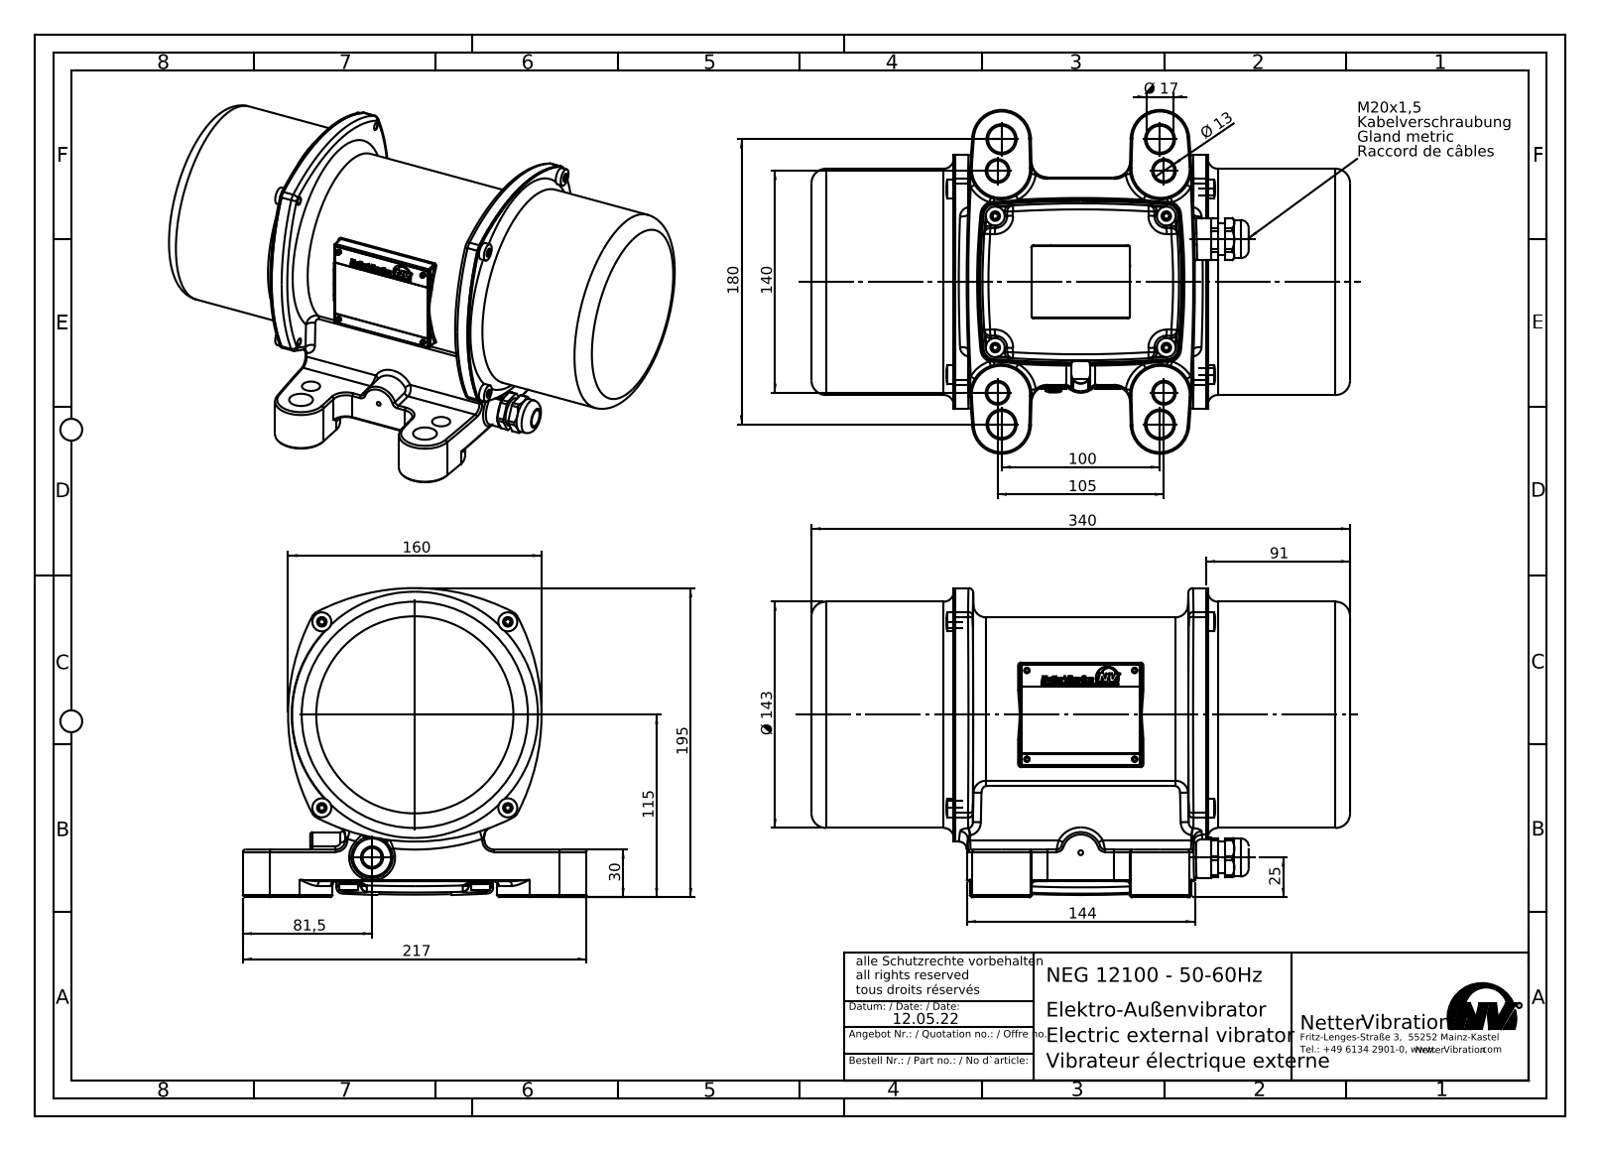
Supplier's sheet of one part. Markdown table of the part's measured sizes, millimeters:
| quantity | value |
| --- | --- |
| part name | NEG 12100-50-60Hz |
| STEP written by | SolidWorks 2015 (AUTOMOTIVE_DESIGN) |
| units | millimeters |
| bodies | 23 solids, 2789 faces (749 planar, 751 cylindrical, 1289 other) |
| overall size | 340 × 217 × 195 |
| volume | 1 494 000 mm³ |
| surface area | 595 544 mm² |
| round holes (diameter × count) | 3.4 × 4, 6.5 × 4, 7 × 4, 13 × 4, 17 × 4, 12 × 2, 14 × 2, 14.5 × 1, 18.5 × 1, 122 × 1, 140.4 × 1 |
| round bosses / shafts (diameter × count) | 12 × 8, 6 × 8, 10 × 3, 5 × 3, 142.8 × 1, 24 × 1, 20 × 1, 16 × 1 |
| partial cylindrical surfaces (radius × count) | 2 × 62, 1 × 34, 0.5 × 33, 1.5 × 16, 3 × 14, 0.25 × 12, 1.75 × 11, 2.25 × 11 |
| main face-to-face distances | 1.2, 338.8, 89.8, 249, 15, 340, 337.6, 91, 247.8, 24 |
| hole center spacings | 83, 20.16, 28.54, 48.66, 104.43, 110.25, 111.51, 114.75 |
